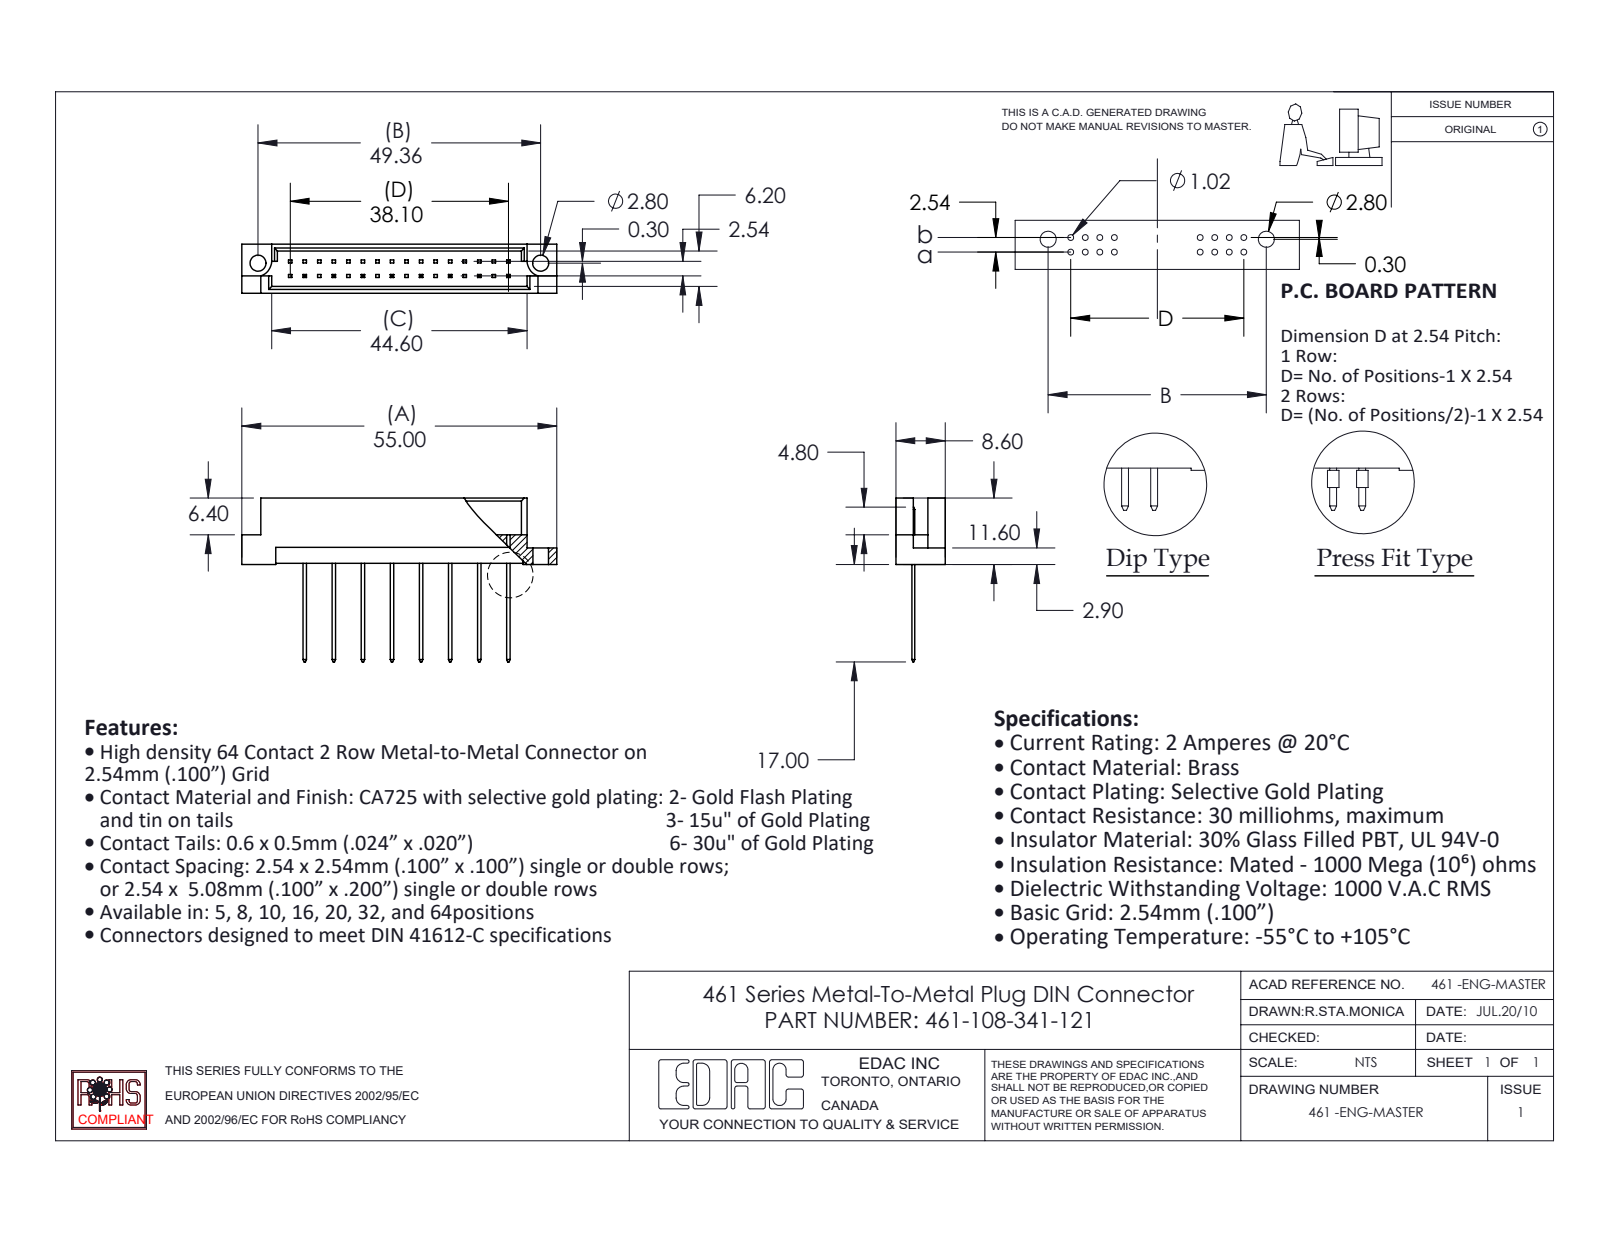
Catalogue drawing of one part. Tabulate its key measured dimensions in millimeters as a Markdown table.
| quantity | value |
| --- | --- |
| part name | 461 Part_32; 461-290_41; 461-108-341-121 |
| STEP written by | SolidWorks 2020 (CONFIG_CONTROL_DESIGN) |
| units | millimeters |
| bodies | 9 solids, 288 faces (282 planar, 6 cylindrical, 0 other) |
| overall size | 55 × 28.6 × 8.6 |
| volume | 2 718 mm³ |
| surface area | 3 720 mm² |
| round holes (diameter × count) | 2.8 × 2 |
| partial cylindrical surfaces (radius × count) | 2.8 × 2 |
| main face-to-face distances | 1.2, 7.4, 8.6, 6.2, 5, 2.78, 5.82, 1.58, 4.62, 3.28 |
| hole center spacings | 49.36 |
